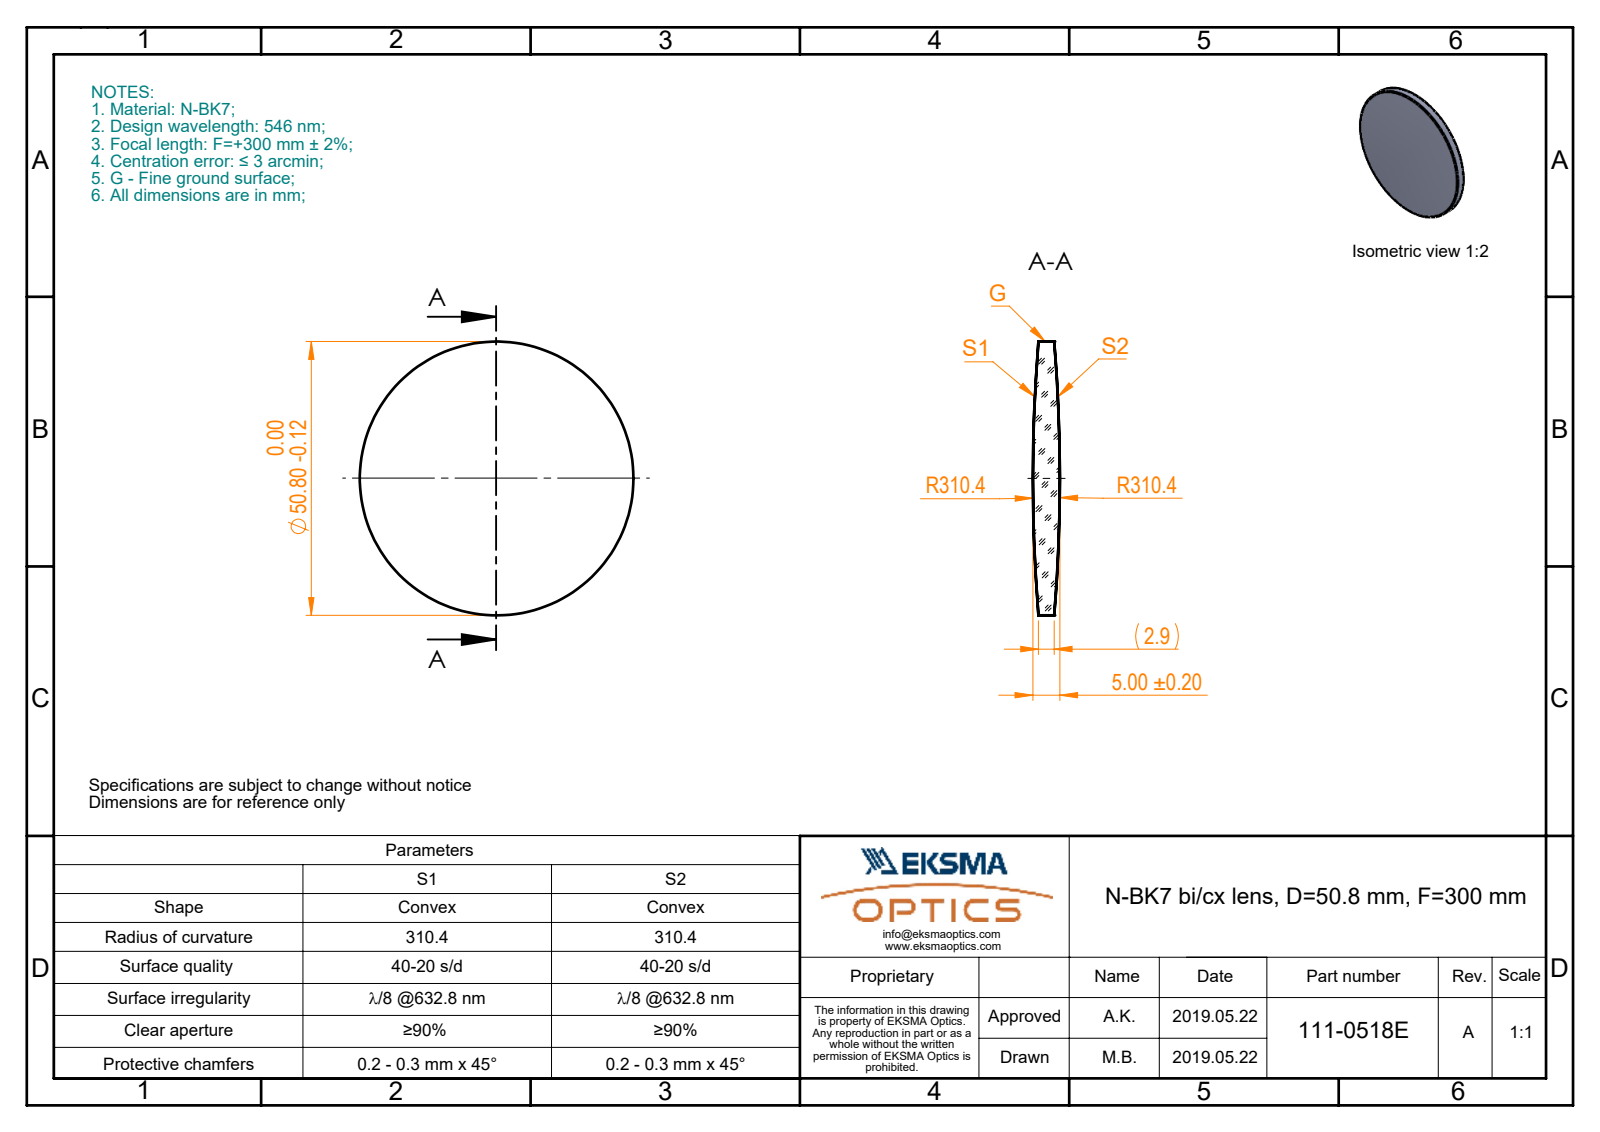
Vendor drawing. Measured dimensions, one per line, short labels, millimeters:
name: 111-0518E BK7 bi-cx 50.8 F300
written by: SolidWorks 2017 (CONFIG_CONTROL_DESIGN)
unit: mm
bodies: 1 solid, 6 faces (0 planar, 2 cylindrical, 4 other)
size: 50.8 × 50.8 × 5
volume: 8 025 mm³; area: 4 526 mm²
bosses: 1× ⌀50.8
